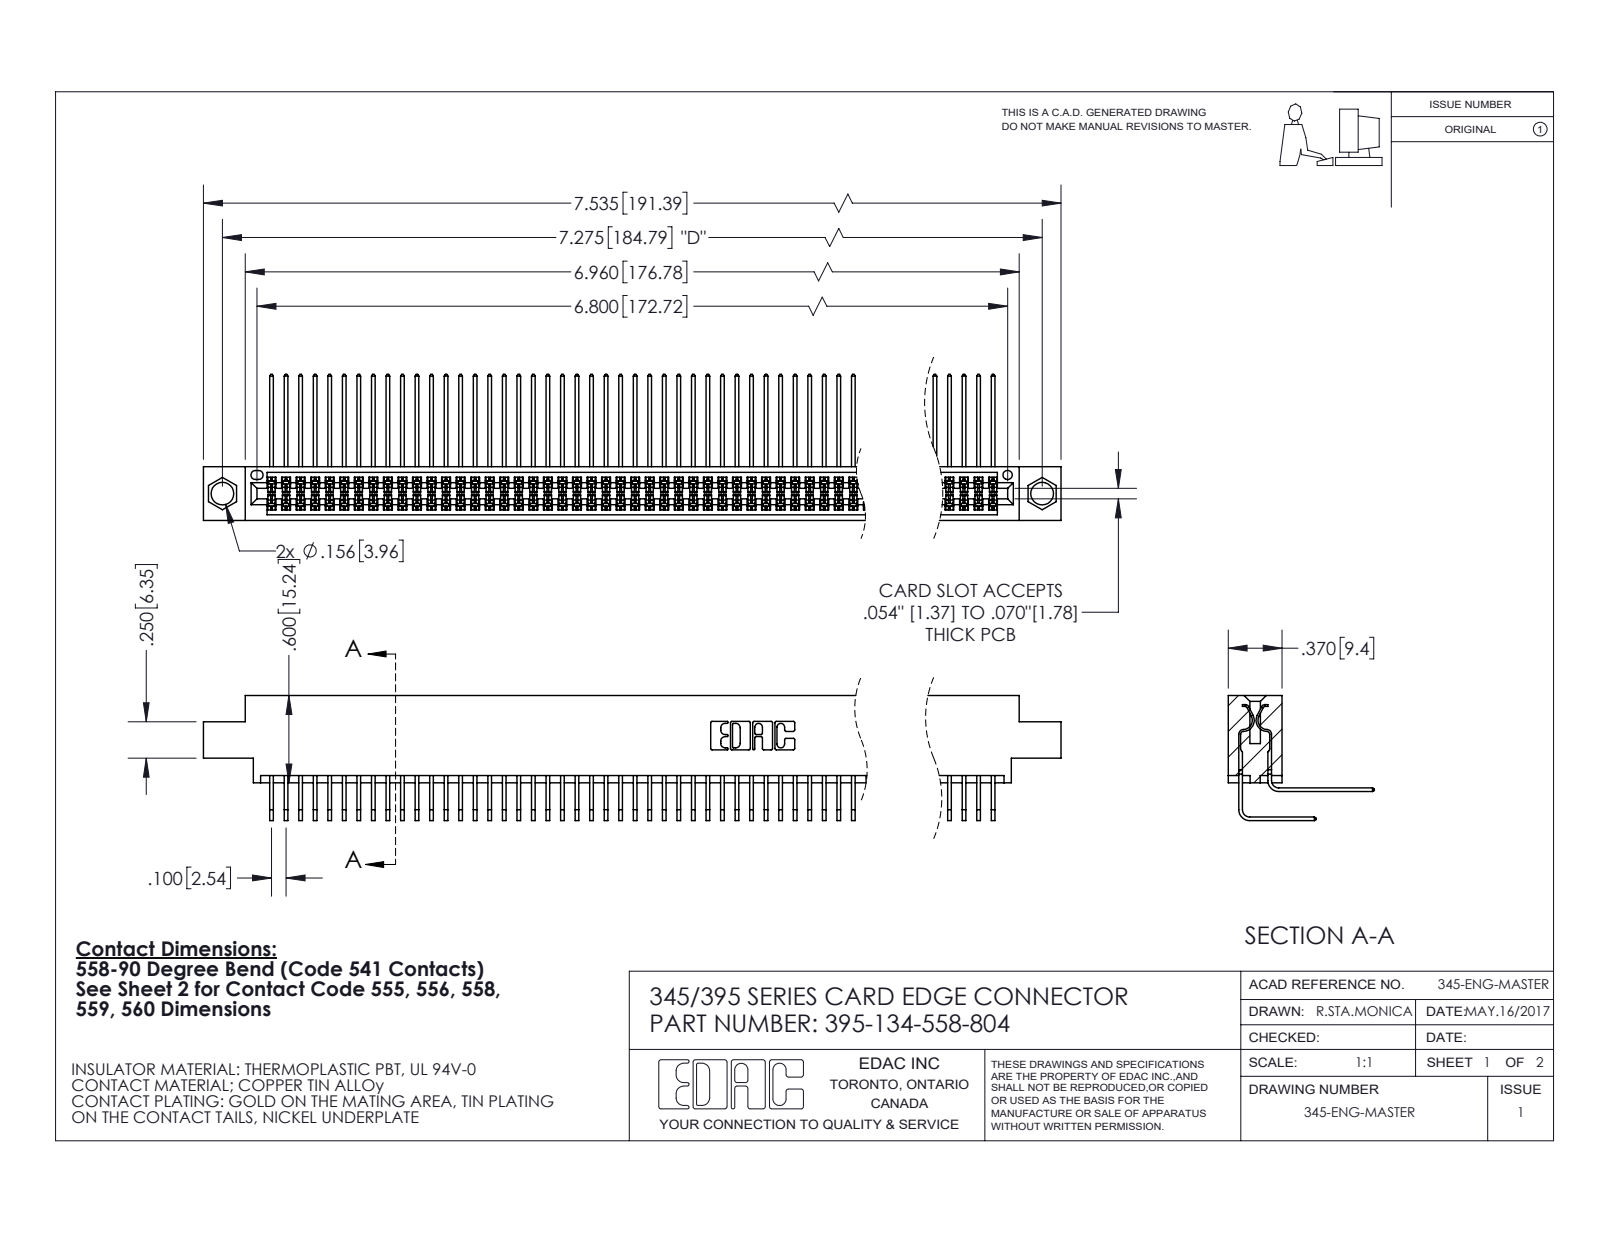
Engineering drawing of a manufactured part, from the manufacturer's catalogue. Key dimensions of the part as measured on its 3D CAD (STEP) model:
Part name (STEP PRODUCT): 345-292-001_558 Tail - 2; 395-134-558-804; 345 Part_0.170 Offset - 0.156 Dia-TI; 345-292-001_558 559 Tail - 1
STEP written by: SolidWorks 2020 (CONFIG_CONTROL_DESIGN)
Units: inches
Bodies: 135 solids, 7112 faces (4788 planar, 2324 cylindrical, 0 other)
Overall size (bounding box): 7.535 × 1.005 × 0.859
Volume: 1.182 in³ · Surface area: 50.77 in²
Round holes (diameter × count): ⌀0.156 ×2, ⌀0.064 ×1
Partial cylindrical surfaces — rounded edges, fillets, slot ends (radius × count): R0.006 ×201, R0.01 ×22, R0.007 ×6, R0.031 ×6, R0.026 ×3, R0.014 ×2, R0.019 ×2, R0.022 ×2
Main face-to-face distances: 0.072, 0.298, 0.2, 0.37, 0.098, 0.272, 0.025, 0.225, 0.175, 0.025
Hole centre spacings: 0.27, 7.039, 7.275
